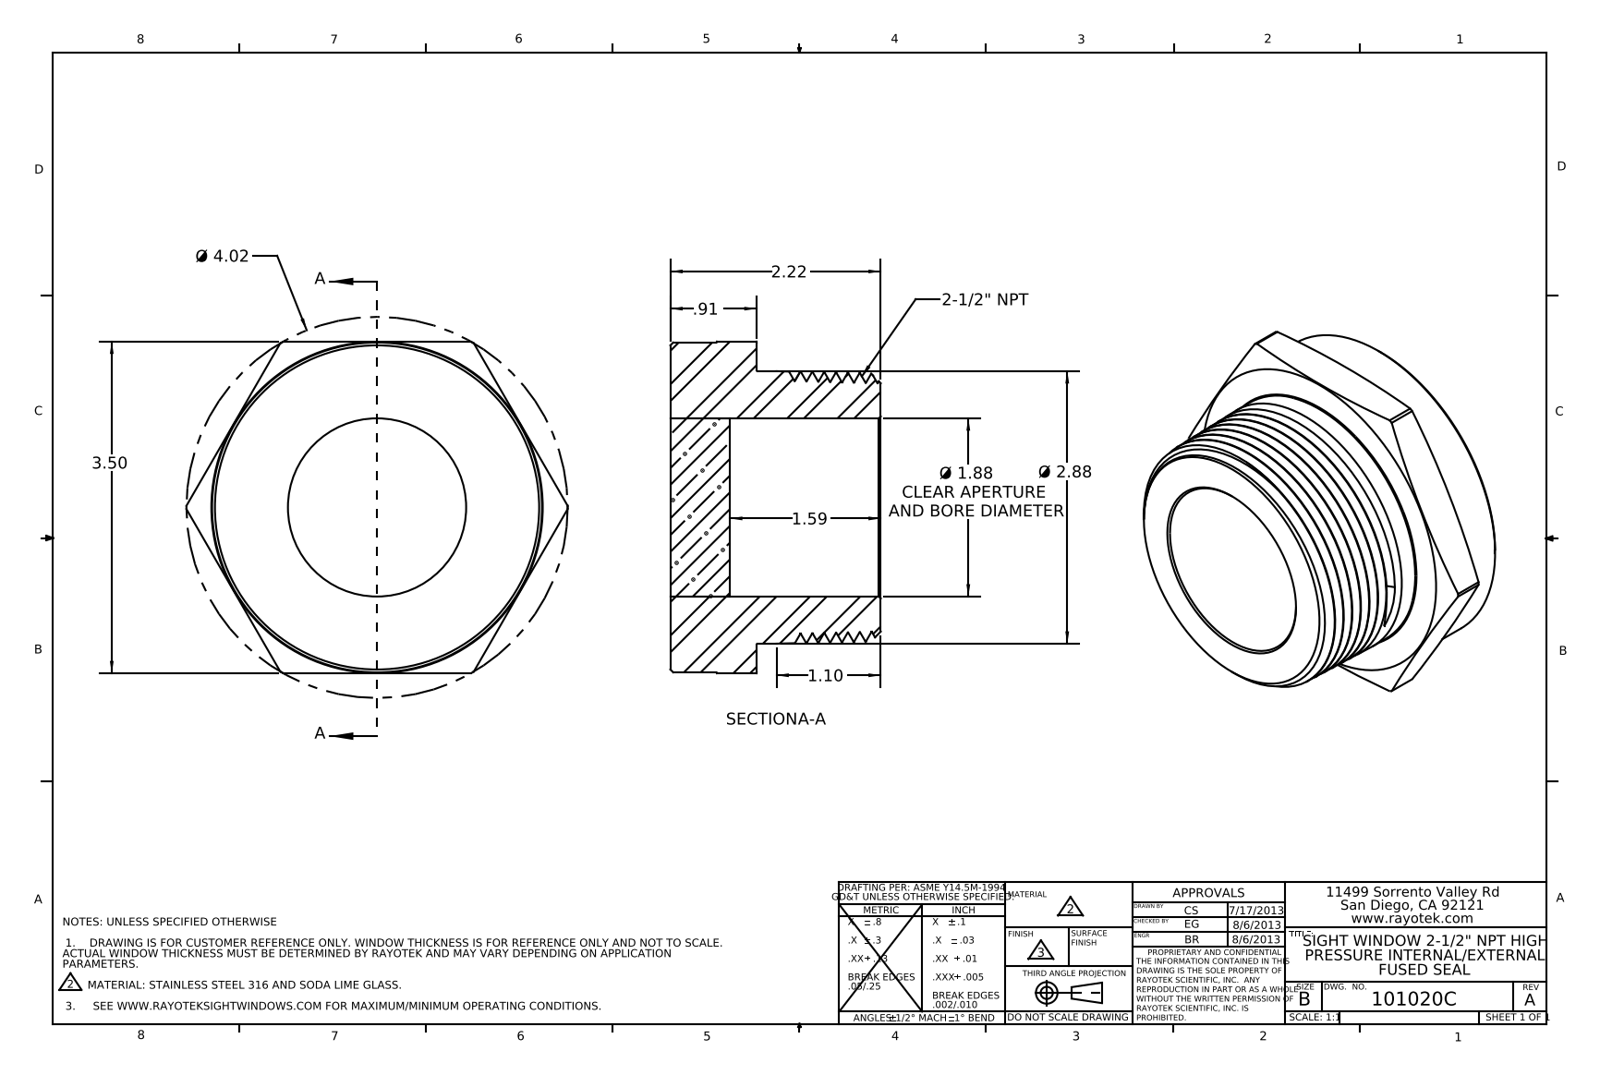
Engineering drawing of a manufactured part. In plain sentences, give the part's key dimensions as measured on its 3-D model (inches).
The part is named "402020; 403020_CUSTOMER; 101020". Its 3-D file was written by "SolidWorks 2012 (AUTOMOTIVE_DESIGN)". It is 2 solids with 62 faces: 14 planar, 15 cylindrical and 33 other. Overall it measures 4.021 by 3.5 by 2.22 inches. Its volume is 12.61 cubic inches and its surface area 65.18 square inches. Round holes: 1 of diameter 1.88. Round bosses or shafts: 1 of diameter 3.48, 1 of diameter 2.875. Partial cylindrical surfaces (rounded edges, fillets, slot ends): 1 of radius 2.011. The main face-to-face distances are 0.91, 0.63, 0.28, 2.22, 1.59, 1.31, 3.5.
